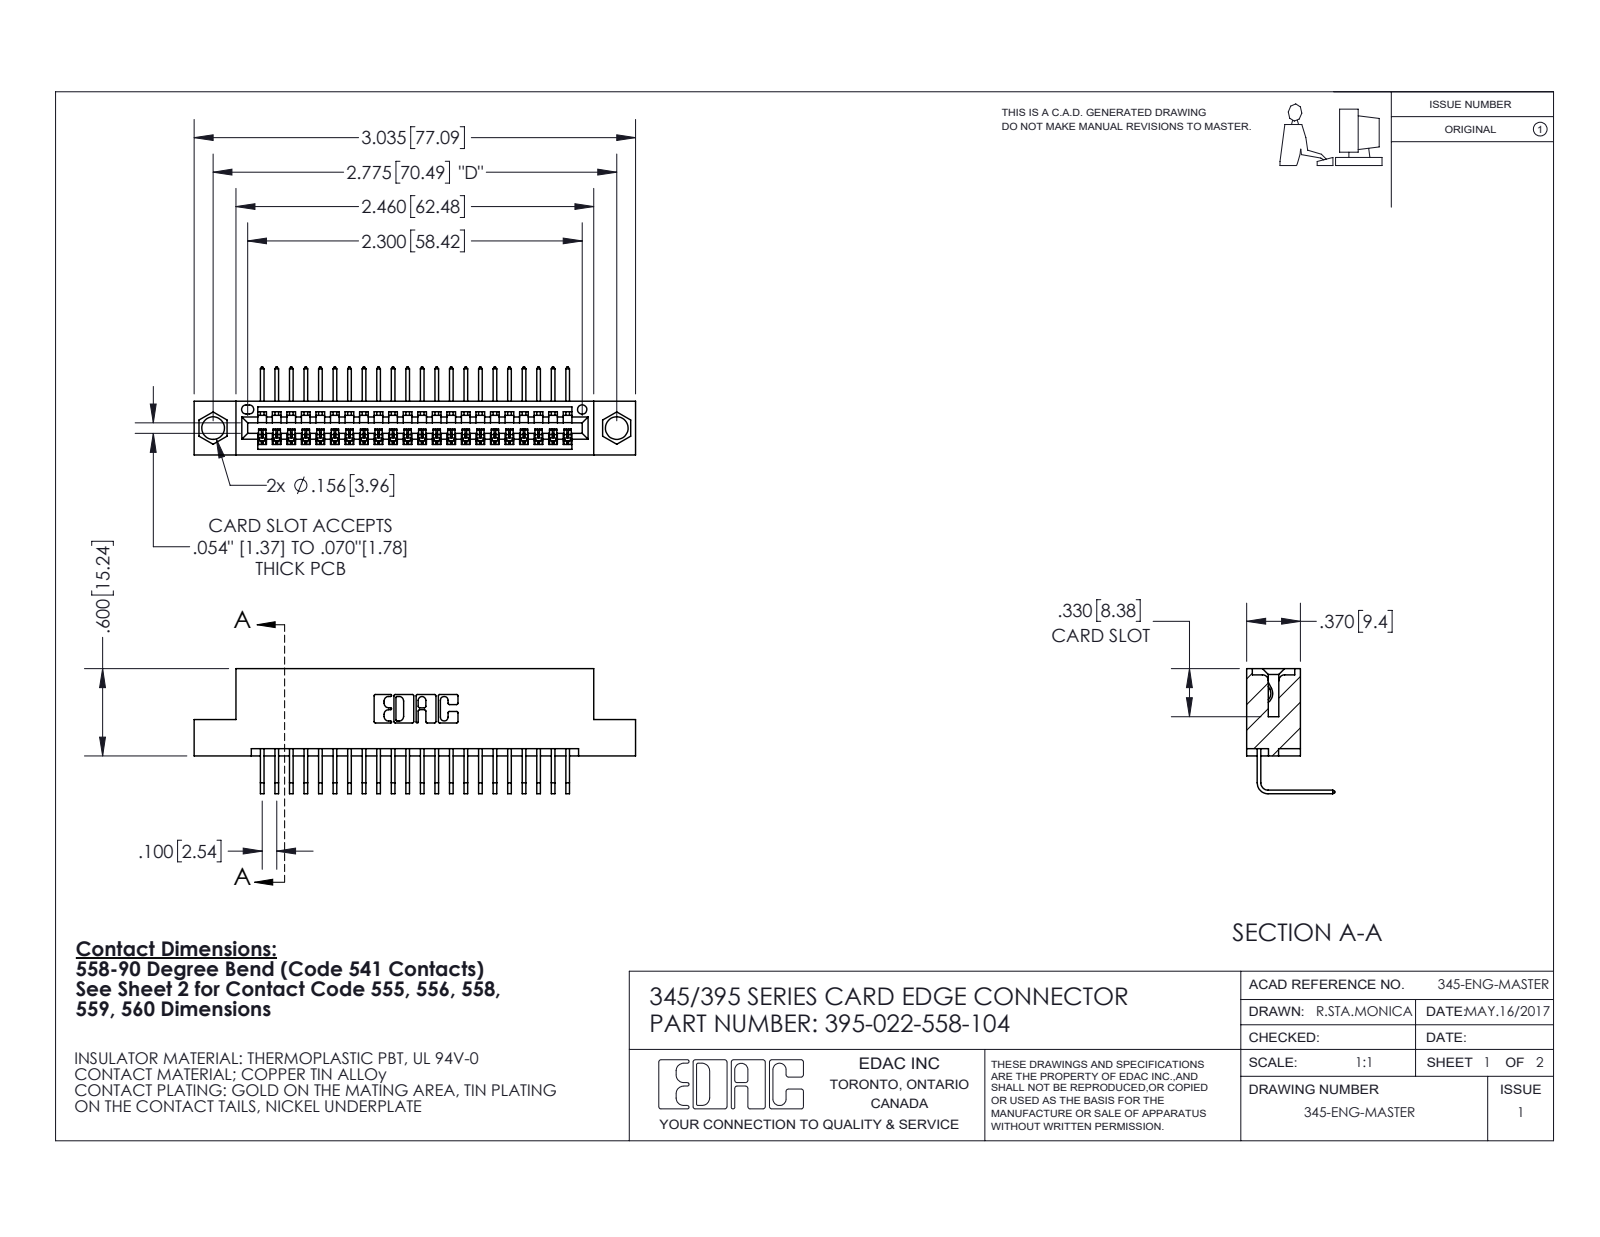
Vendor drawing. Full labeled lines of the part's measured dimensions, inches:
Part name (STEP PRODUCT): 345 Part_Flush Mounting Lugs - 0.156 Dia-TI; 345-292-001_558 Tail - 2; 395-022-558-104
STEP written by: SolidWorks 2020 (CONFIG_CONTROL_DESIGN)
Units: inches
Bodies: 23 solids, 1460 faces (1018 planar, 442 cylindrical, 0 other)
Overall size (bounding box): 3.035 × 0.859 × 0.605
Volume: 0.435 in³ · Surface area: 14.68 in²
Round holes (diameter × count): ⌀0.156 ×2, ⌀0.064 ×1
Partial cylindrical surfaces — rounded edges, fillets, slot ends (radius × count): R0.006 ×44, R0.01 ×22, R0.007 ×6, R0.031 ×6, R0.026 ×3, R0.031 ×2, R0.04 ×2, R0.014 ×1
Main face-to-face distances: 0.072, 0.298, 0.2, 0.37, 0.098, 0.272, 0.025, 0.225, 0.149, 0.072
Hole centre spacings: 0.27, 2.541, 2.775
